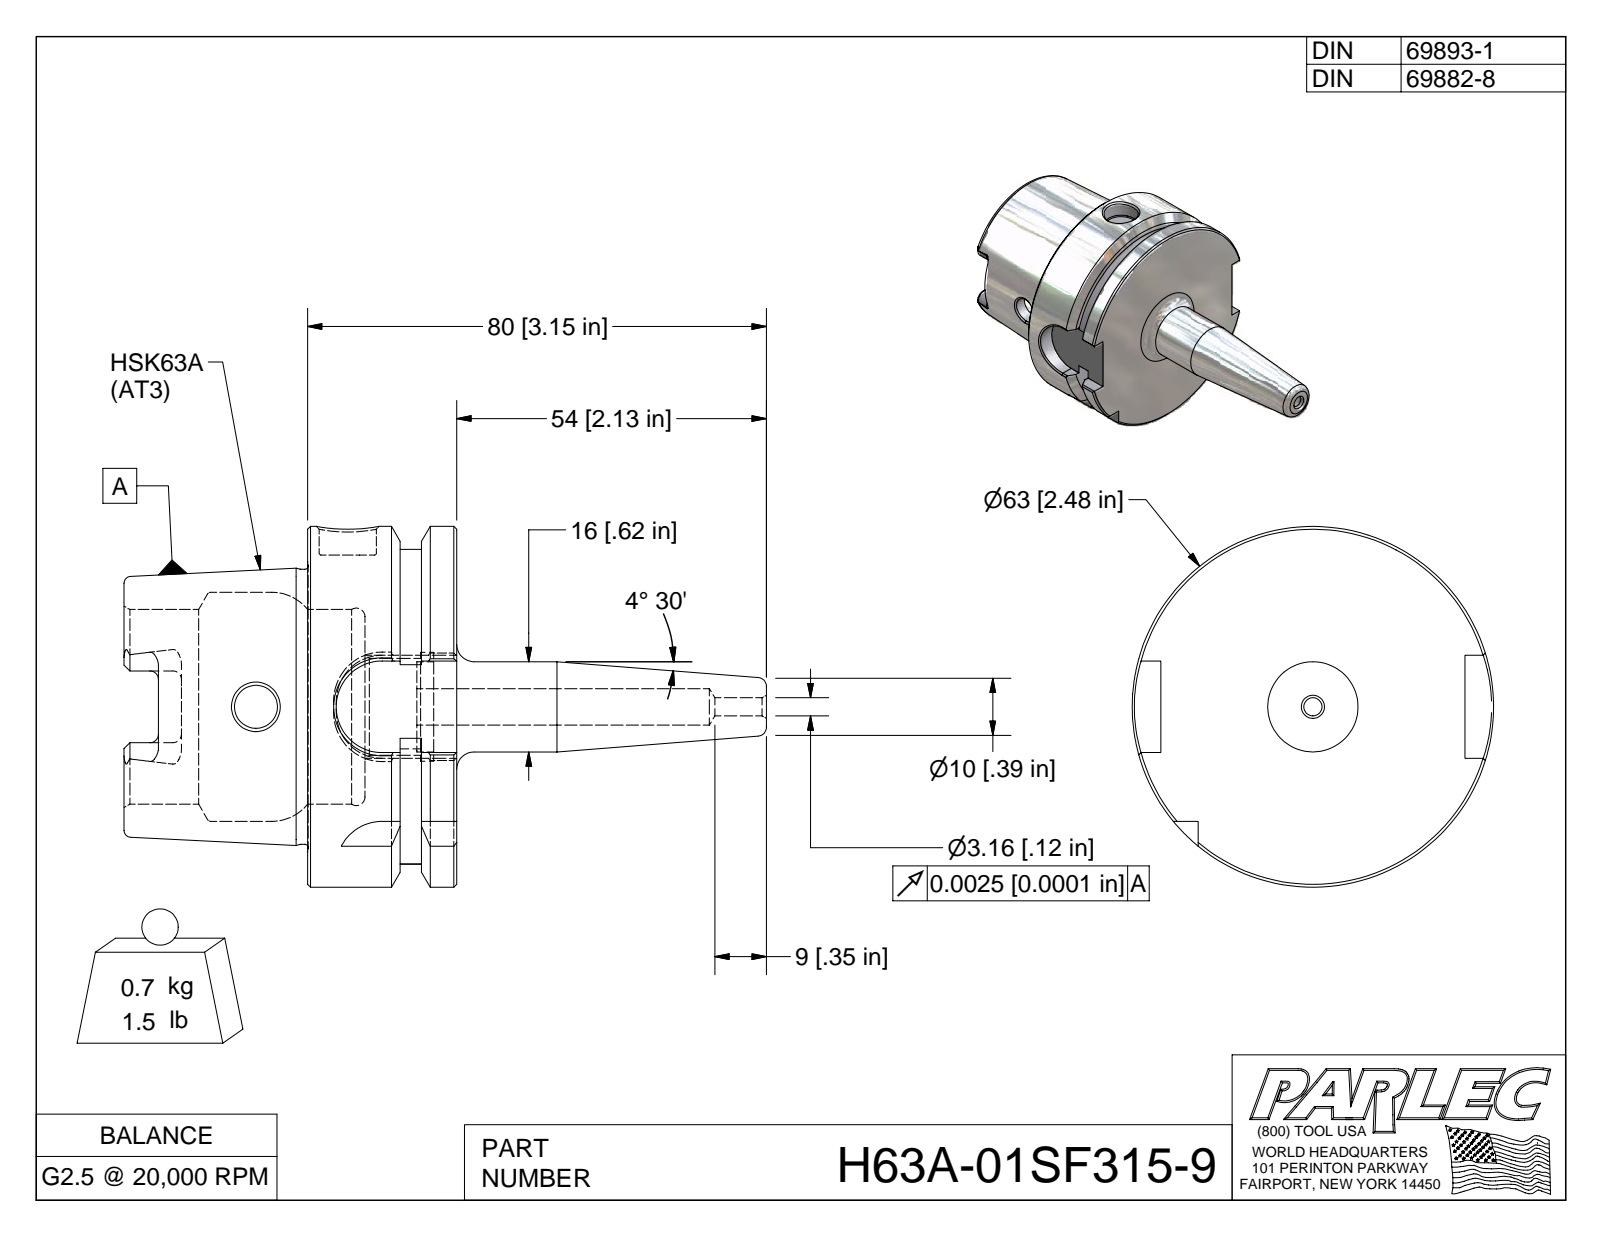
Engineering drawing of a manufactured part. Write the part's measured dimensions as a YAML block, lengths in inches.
part_name: "H63A-01SF315-9; H63A-01SF315-9-1"
step_written_by: "Autodesk Inventor 2009 (AUTOMOTIVE_DESIGN)"
units: inches
bodies: {solids: 1, faces: 136, planar: 48, cylindrical: 34, other: 54}
overall_size: [4.409, 2.48, 2.48]
volume: 5.399
surface_area: 40.15
round_holes:
  - {diameter: 0.124, count: 1}
  - {diameter: 0.295, count: 1}
  - {diameter: 0.394, count: 1}
  - {diameter: 0.666, count: 1}
  - {diameter: 0.749, count: 1}
  - {diameter: 1.339, count: 1}
  - {diameter: 1.575, count: 1}
round_bosses_or_shafts:
  - {diameter: 2.48, count: 1}
  - {diameter: 1.891, count: 1}
  - {diameter: 0.62, count: 1}
partial_cylinders:
  - {radius: 0.059, count: 6}
  - {radius: 0.113, count: 4}
  - {radius: 0.315, count: 4}
  - {radius: 1.083, count: 1}
face_to_face_distances: [1.024, 0.241, 0.389, 0.394, 0.63, 1.26, 2.283, 1.654, 1.894, 0.635]
